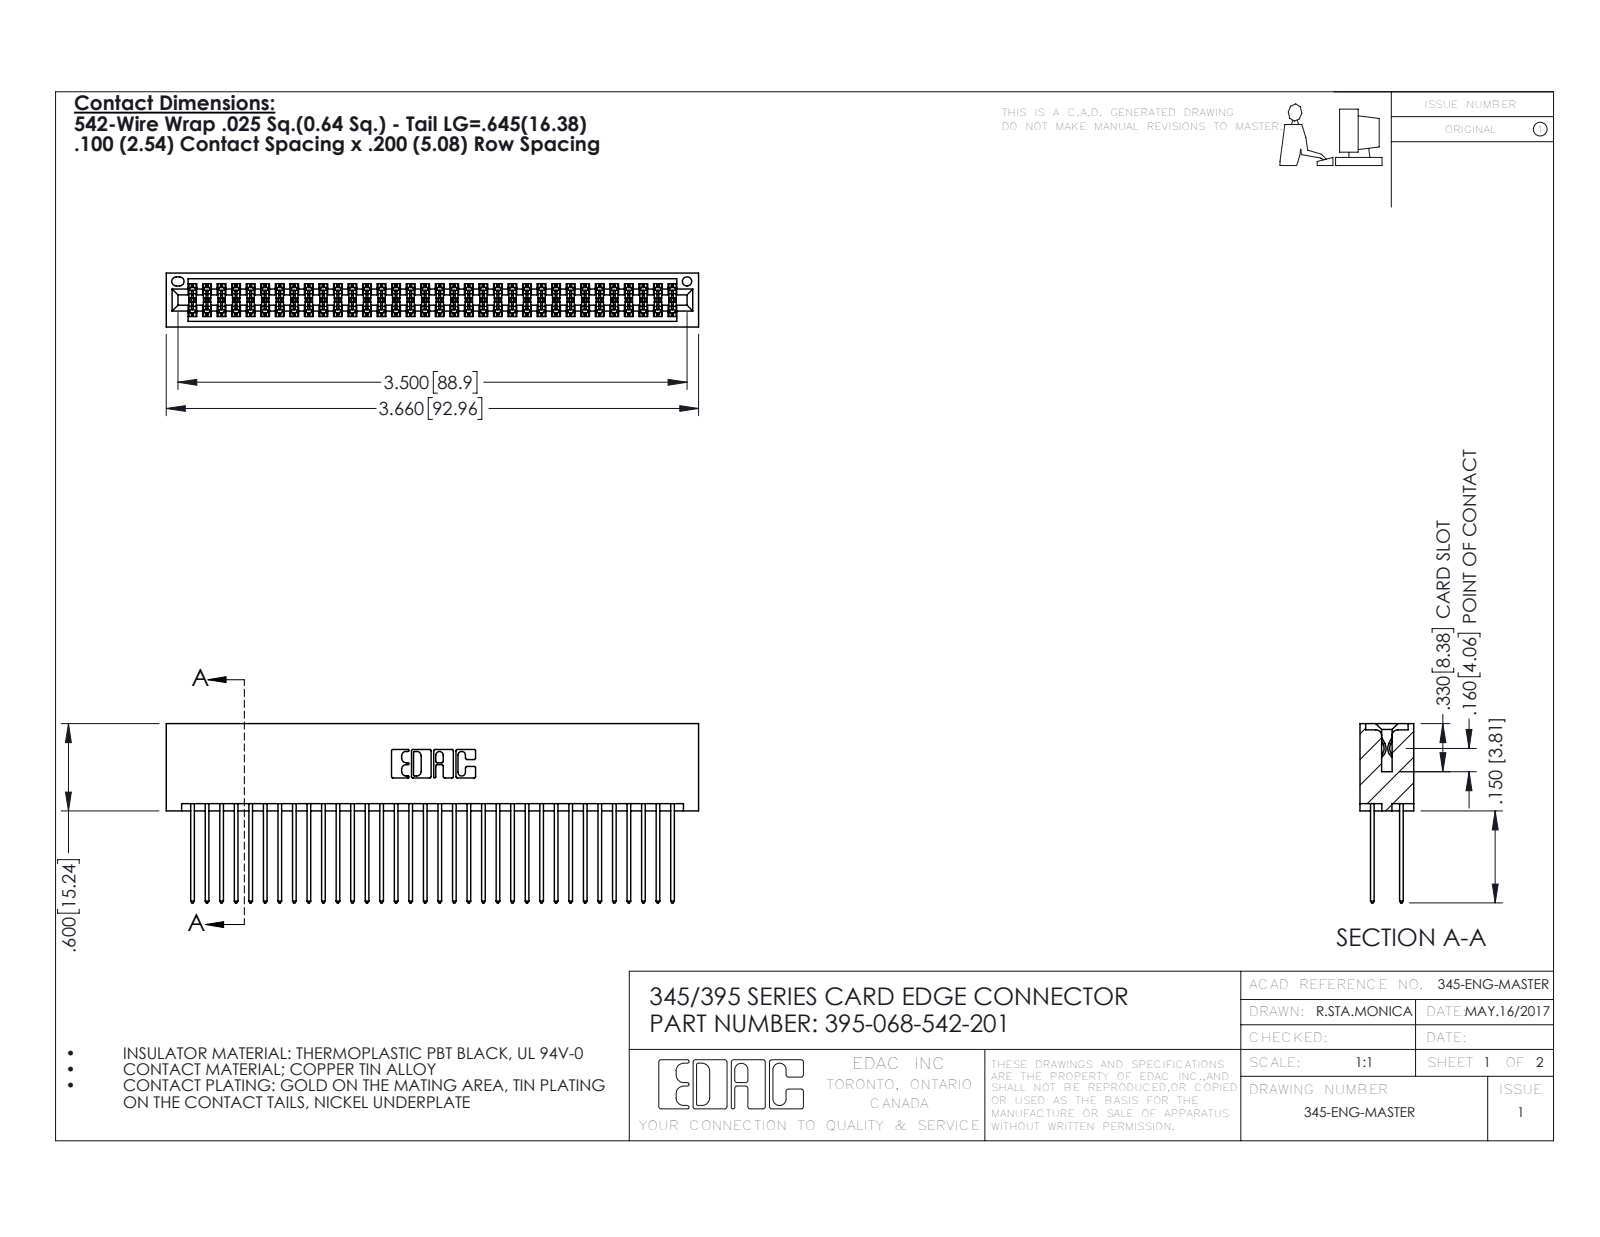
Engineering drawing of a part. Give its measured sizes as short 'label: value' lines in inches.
name: 395-068-542-201; 345-292-001_345-293-142; 345 Part_No Mounting Lugs
written by: SolidWorks 2016 (CONFIG_CONTROL_DESIGN)
unit: in
bodies: 69 solids, 3518 faces (2320 planar, 1198 cylindrical, 0 other)
size: 3.66 × 1.232 × 0.37
volume: 0.603 in³; area: 25.18 in²
holes: 1× ⌀0.064
rounds: 102× R0.006, 68× R0.01, 22× R0.01, 6× R0.007, 6× R0.031, 3× R0.026, 2× R0.014, 2× R0.019
face distances: 0.298, 0.072, 0.2, 0.098, 0.272, 0.025, 0.225, 0.37, 0.175, 0.149
